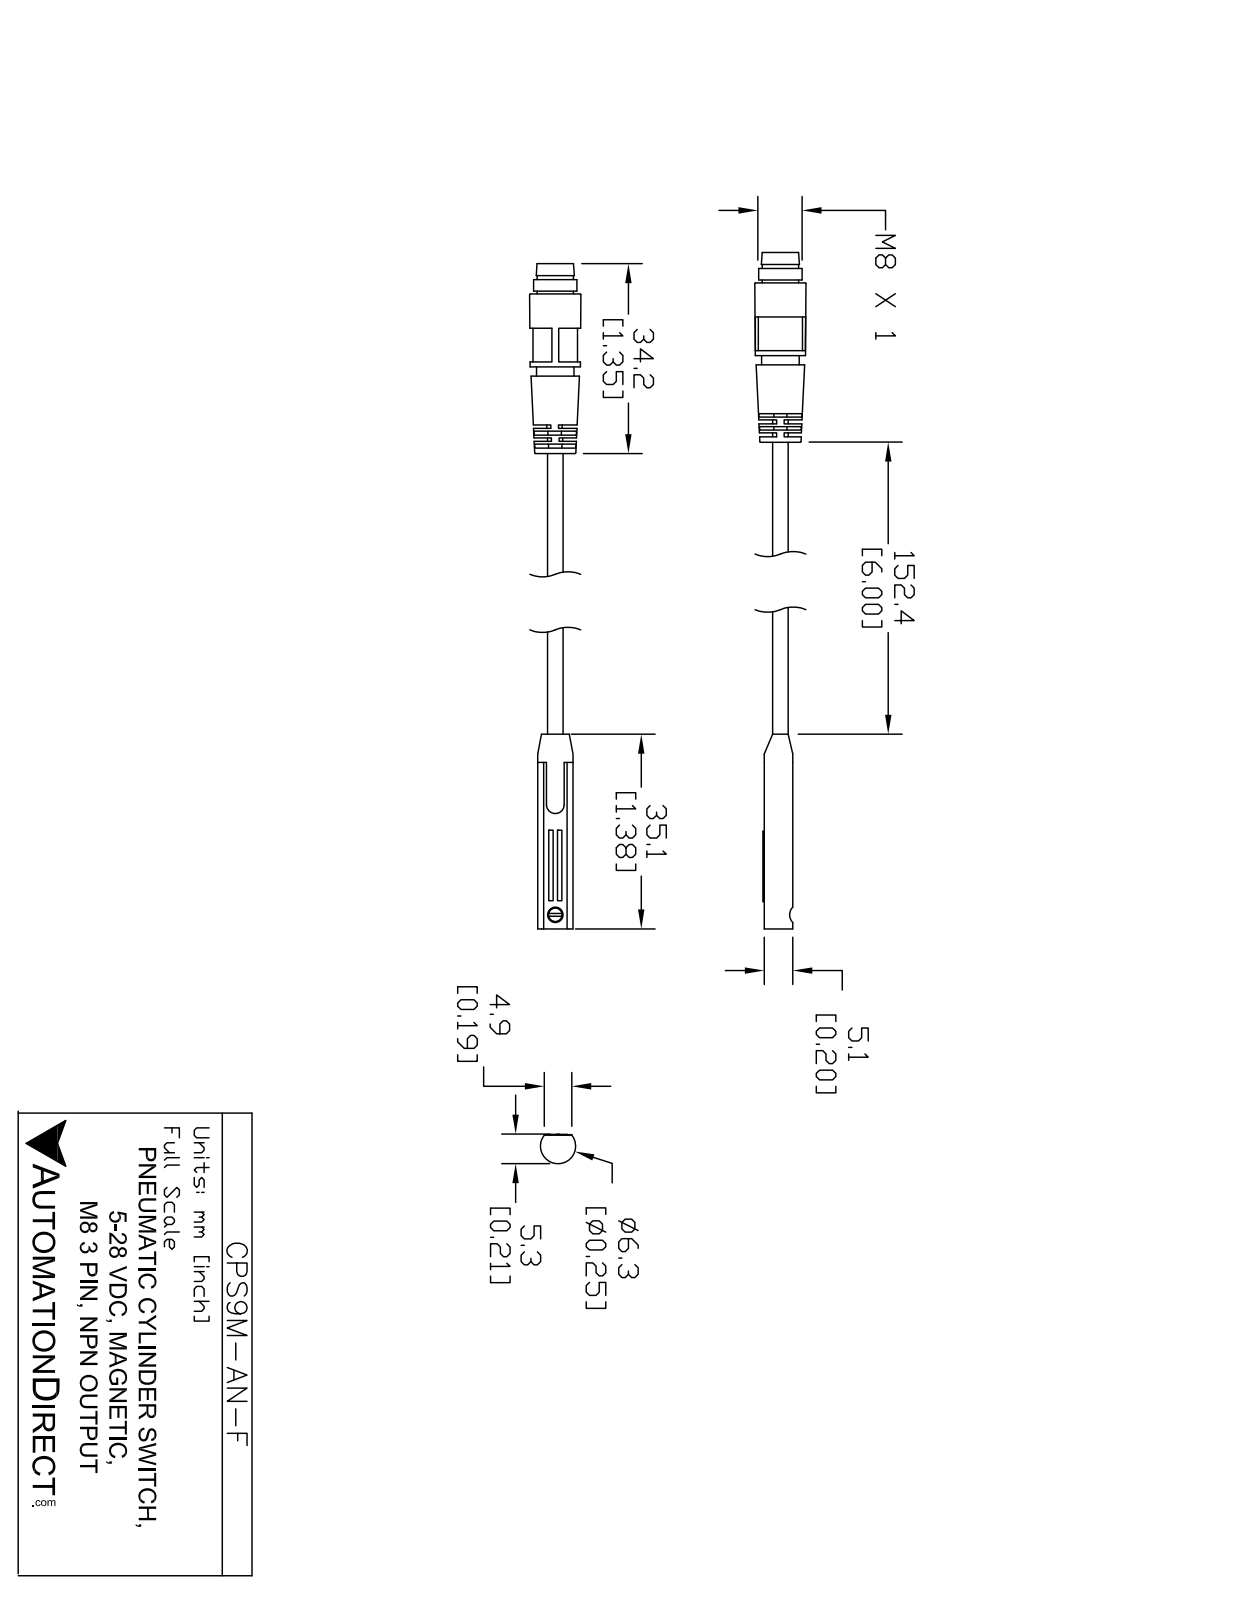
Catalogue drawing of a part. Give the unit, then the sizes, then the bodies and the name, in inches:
Units: inches
Overall size (bounding box): 5.682 × 0.25 × 0.21
Round holes (diameter × count): ⌀0.031 ×1, ⌀0.104 ×1
Round bosses / shafts (diameter × count): ⌀0.138 ×1, ⌀0.105 ×1
Partial cylindrical surfaces — rounded edges, fillets, slot ends (radius × count): R0.005 ×13, R0.015 ×3, R0.031 ×2, R0.045 ×1, R0.062 ×1, R0.105 ×1, R0.125 ×1
Main face-to-face distances: 0.168, 0.02, 0.021, 0.146, 0.062, 0.042, 0.029, 0.071, 0.091, 1.18
Hole centre spacings: 0.136
Volume: 0.075 in³ · Surface area: 3.88 in²
Bodies: 4 solids, 122 faces (48 planar, 50 cylindrical, 24 other)
Part name (STEP PRODUCT): CPS9M-AN-F
STEP written by: SolidWorks 2017 (AUTOMOTIVE_DESIGN)
